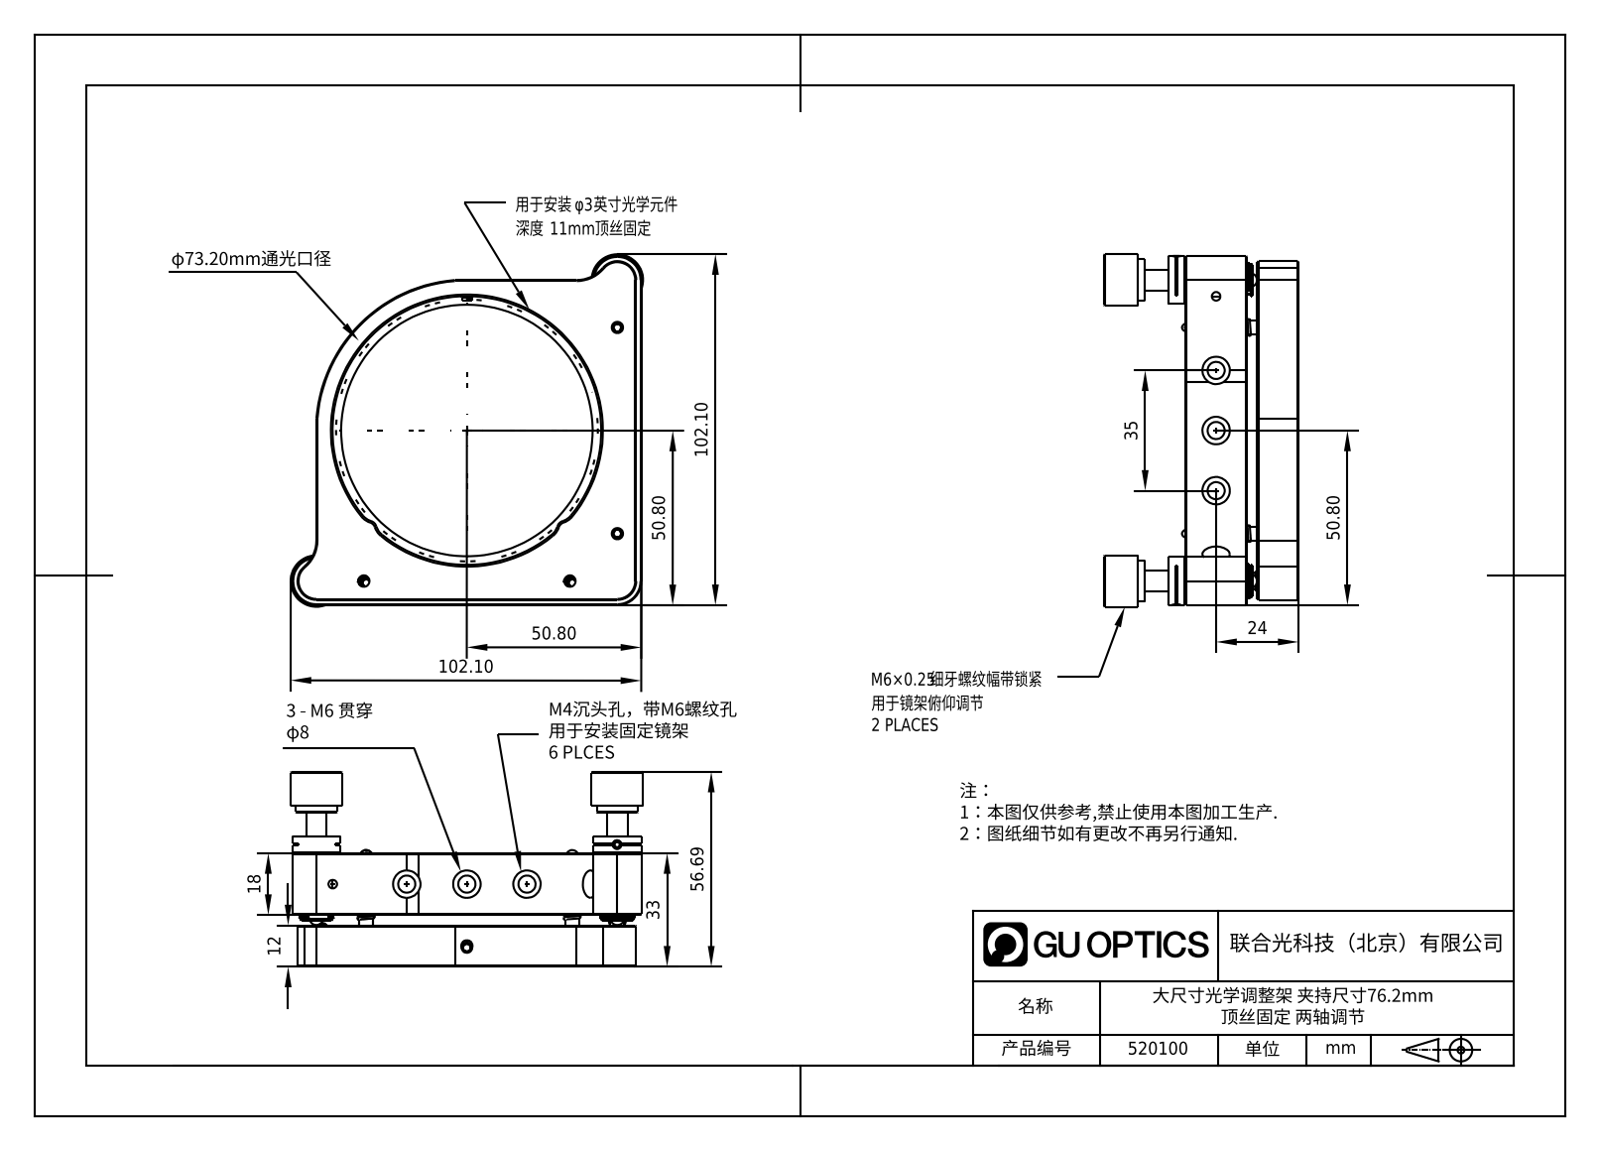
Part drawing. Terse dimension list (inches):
name: 520100
written by: SolidWorks 2020 (CONFIG_CONTROL_DESIGN)
unit: in
bodies: 0 solids, 585 faces (269 planar, 152 cylindrical, 164 other)
size: 4.039 × 4.039 × 2.185
holes: 7× ⌀0.197, 6× ⌀0.256, 6× ⌀0.315, 5× ⌀0.098, 5× ⌀0.13, 2× ⌀0.157, 2× ⌀0.236, 1× ⌀0.047, 1× ⌀0.374, 1× ⌀2.882, 1× ⌀3.079
bosses: 7× ⌀0.157, 6× ⌀0.118, 4× ⌀0.079, 2× ⌀0.591, 2× ⌀0.551, 2× ⌀0.472, 2× ⌀0.374, 2× ⌀0.315
rounds: 24× R0.008, 8× R0.041, 6× R0.197, 4× R0.02, 4× R0.394, 3× R0.217, 2× R0.098, 2× R0.157
face distances: 0.472, 1.339, 0.866, 0.63, 0.157, 0.709, 0.059, 0.039, 0.197, 0.492
hole spacings: 0.543, 0.689, 2.09, 2.906, 0.848, 1.537, 2.226, 2.439
